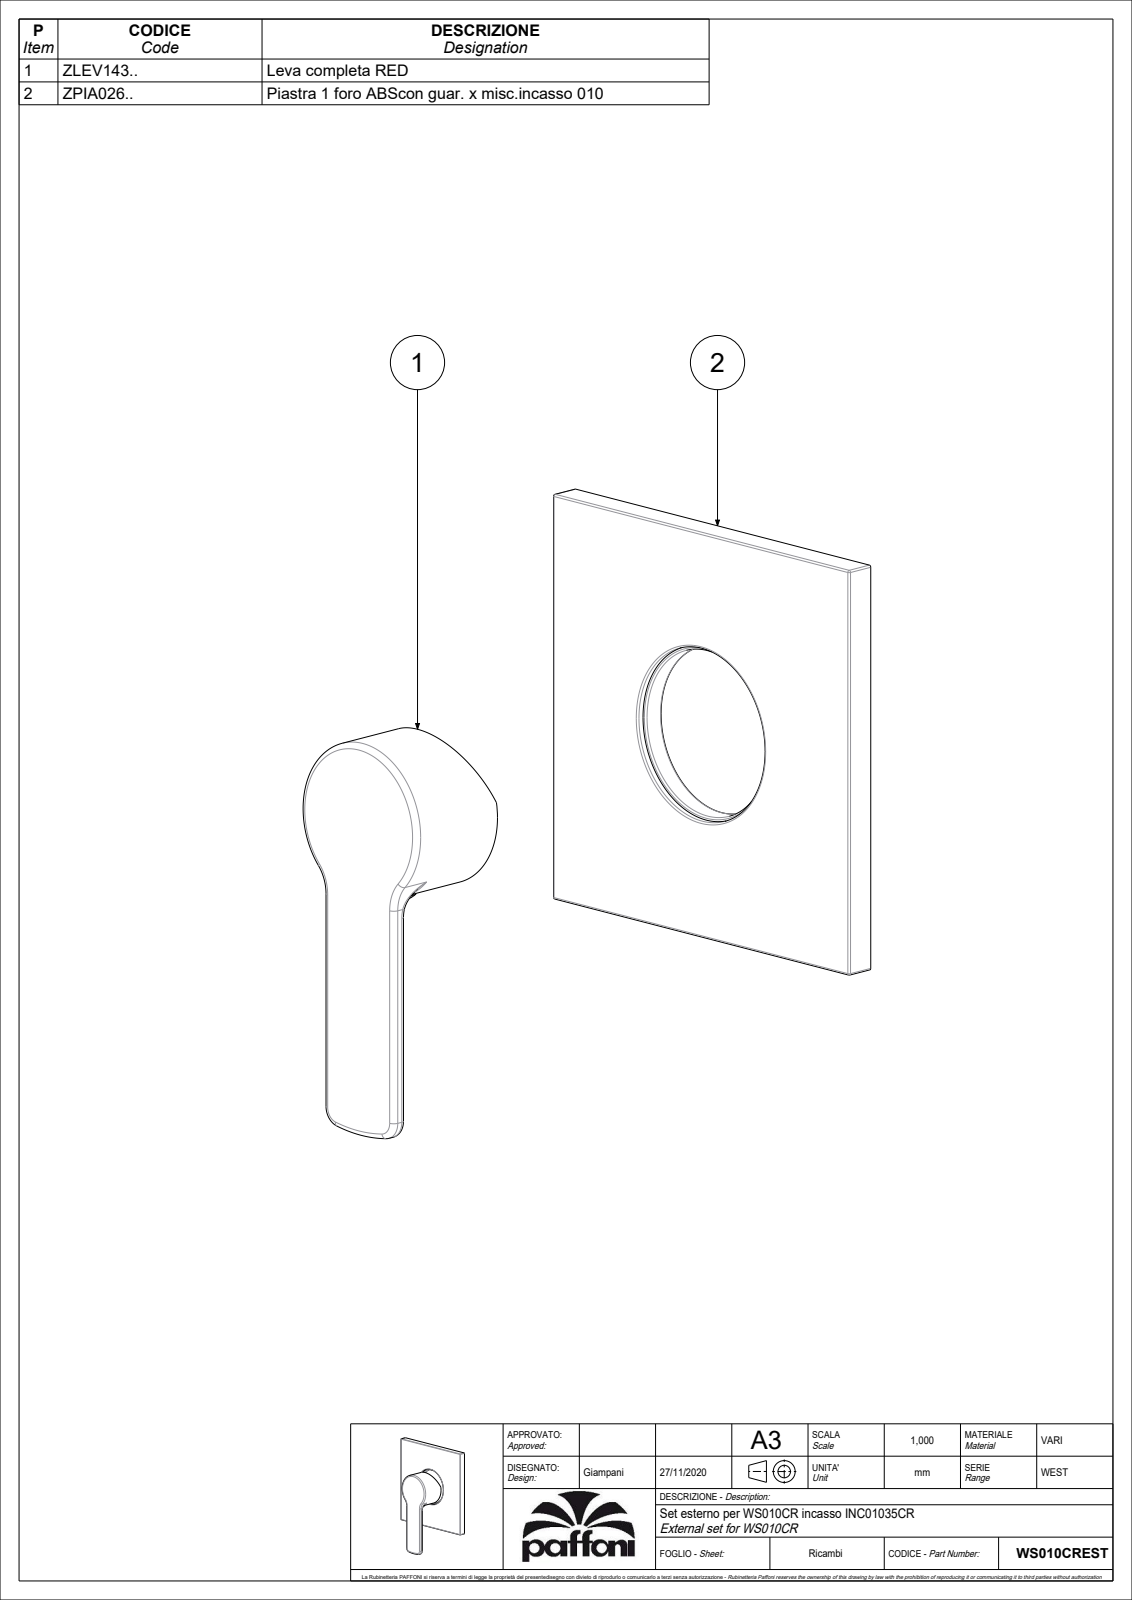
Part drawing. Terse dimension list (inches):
name: WS010CREST
written by: CREO PARAMETRIC BY PTC INC, 2020044 (CONFIG_CONTROL_DESIGN)
unit: in
bodies: 2 solids, 316 faces (90 planar, 115 cylindrical, 111 other)
size: 5.512 × 4.331 × 1.584
volume: 5.086 in³; area: 75.04 in²
holes: 1× ⌀0.118, 1× ⌀0.13, 1× ⌀0.177, 1× ⌀1.772, 1× ⌀1.85, 1× ⌀1.929
bosses: 1× ⌀2.008, 1× ⌀1.693, 1× ⌀0.299, 1× ⌀0.217, 1× ⌀0.197
rounds: 55× R0.02, 4× R0.039, 4× R0.059, 4× R0.079, 2× R0.197, 2× R0.394, 1× R1.969
face distances: 0.276, 0.079, 0.197, 4.252, 0.098, 1.358, 4.232, 0.02, 4.154, 1.161
